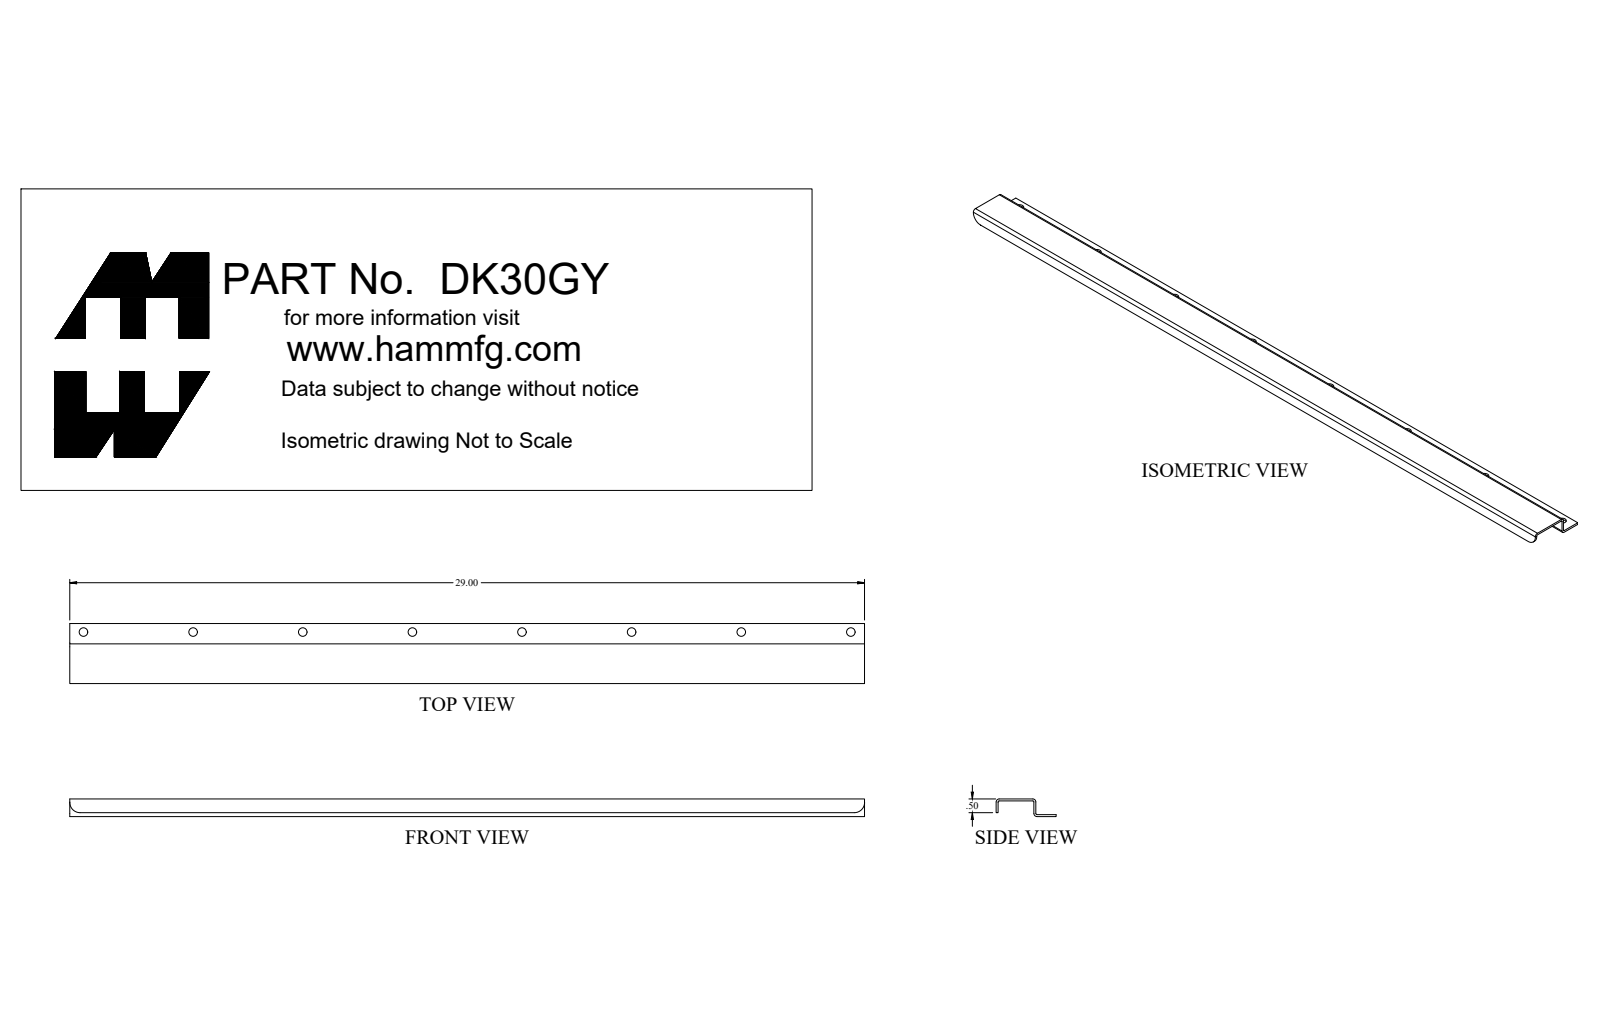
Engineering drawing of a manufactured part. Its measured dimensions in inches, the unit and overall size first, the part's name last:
Units: inches
Overall size (bounding box): 29 × 2.188 × 1.322
Round holes (diameter × count): ⌀0.313 ×8, ⌀0.201 ×1, ⌀0.275 ×1
Round bosses / shafts (diameter × count): ⌀0.625 ×1, ⌀0.483 ×1, ⌀0.25 ×1
Partial cylindrical surfaces — rounded edges, fillets, slot ends (radius × count): R0.036 ×3, R0.108 ×3, R0.375 ×2
Main face-to-face distances: 0.072, 0.572, 0.644, 1.376, 0.5, 0.063, 0.635, 0.707, 0.135, 1.448
Hole centre spacings: 4, 8, 12, 16, 20, 24, 28
Volume: 7.896 in³ · Surface area: 233.3 in²
Bodies: 5 solids, 75 faces (35 planar, 34 cylindrical, 6 other)
Part name (STEP PRODUCT): DK30GY_Default
STEP written by: SolidWorks 2018 (CONFIG_CONTROL_DESIGN)
